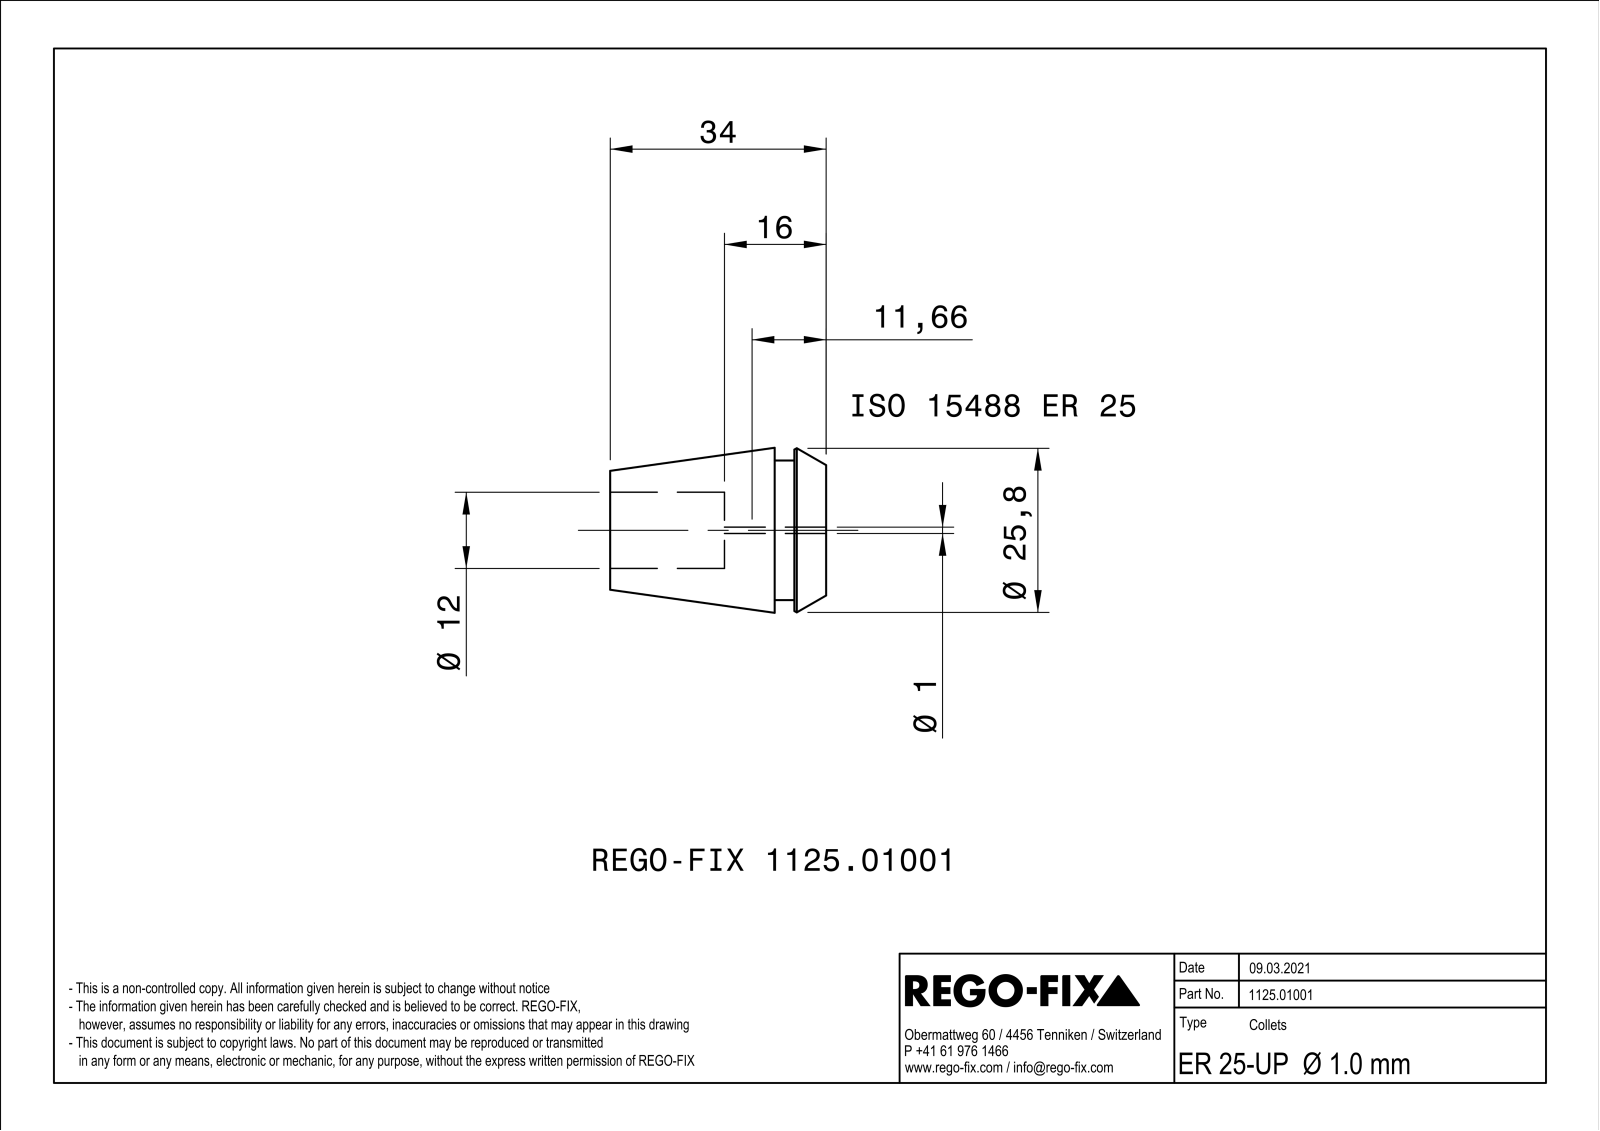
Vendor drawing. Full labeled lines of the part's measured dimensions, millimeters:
Part name (STEP PRODUCT): NOCUT
STEP written by: SIEMENS PLM Software Solid Edge ST10 (AUTOMOTIVE_DESIGN)
Units: millimetres
Bodies: 1 solid, 268 faces (100 planar, 56 cylindrical, 112 other)
Overall size (bounding box): 34 × 25.99 × 25.99
Volume: 9 213 mm³ · Surface area: 9 348 mm²
Round holes (diameter × count): ⌀12 ×1
Round bosses / shafts (diameter × count): ⌀22 ×1
Partial cylindrical surfaces — rounded edges, fillets, slot ends (radius × count): R0.4 ×14, R40 ×8, R0.5 ×1
Main face-to-face distances: 0.8, 0.78, 0.82, 0.63, 8.1, 34, 25.9, 5, 3.1, 29
